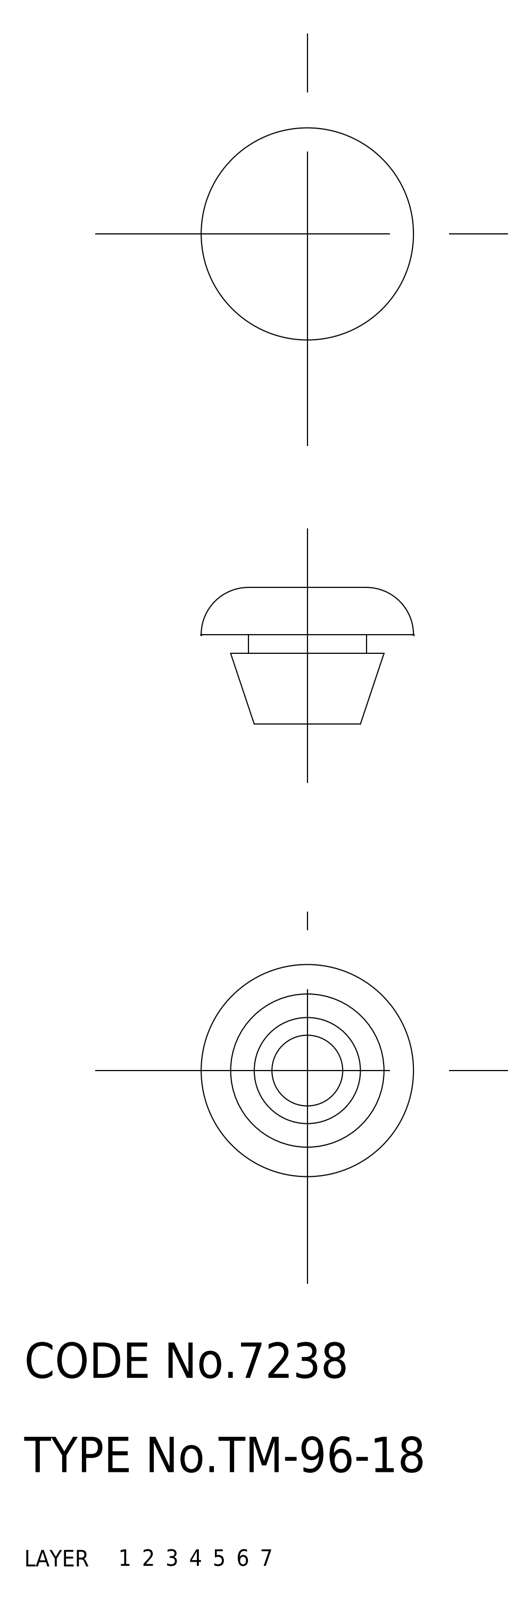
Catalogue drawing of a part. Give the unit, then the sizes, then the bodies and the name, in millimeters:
Units: millimetres
Overall size (bounding box): 18 × 18 × 11.6
Volume: 1 336 mm³ · Surface area: 1 082 mm²
Bodies: 1 solid, 13 faces (0 planar, 0 cylindrical, 13 other)
Part name (STEP PRODUCT): cushion
STEP written by: CADfix (AUTOMOTIVE_DESIGN)
